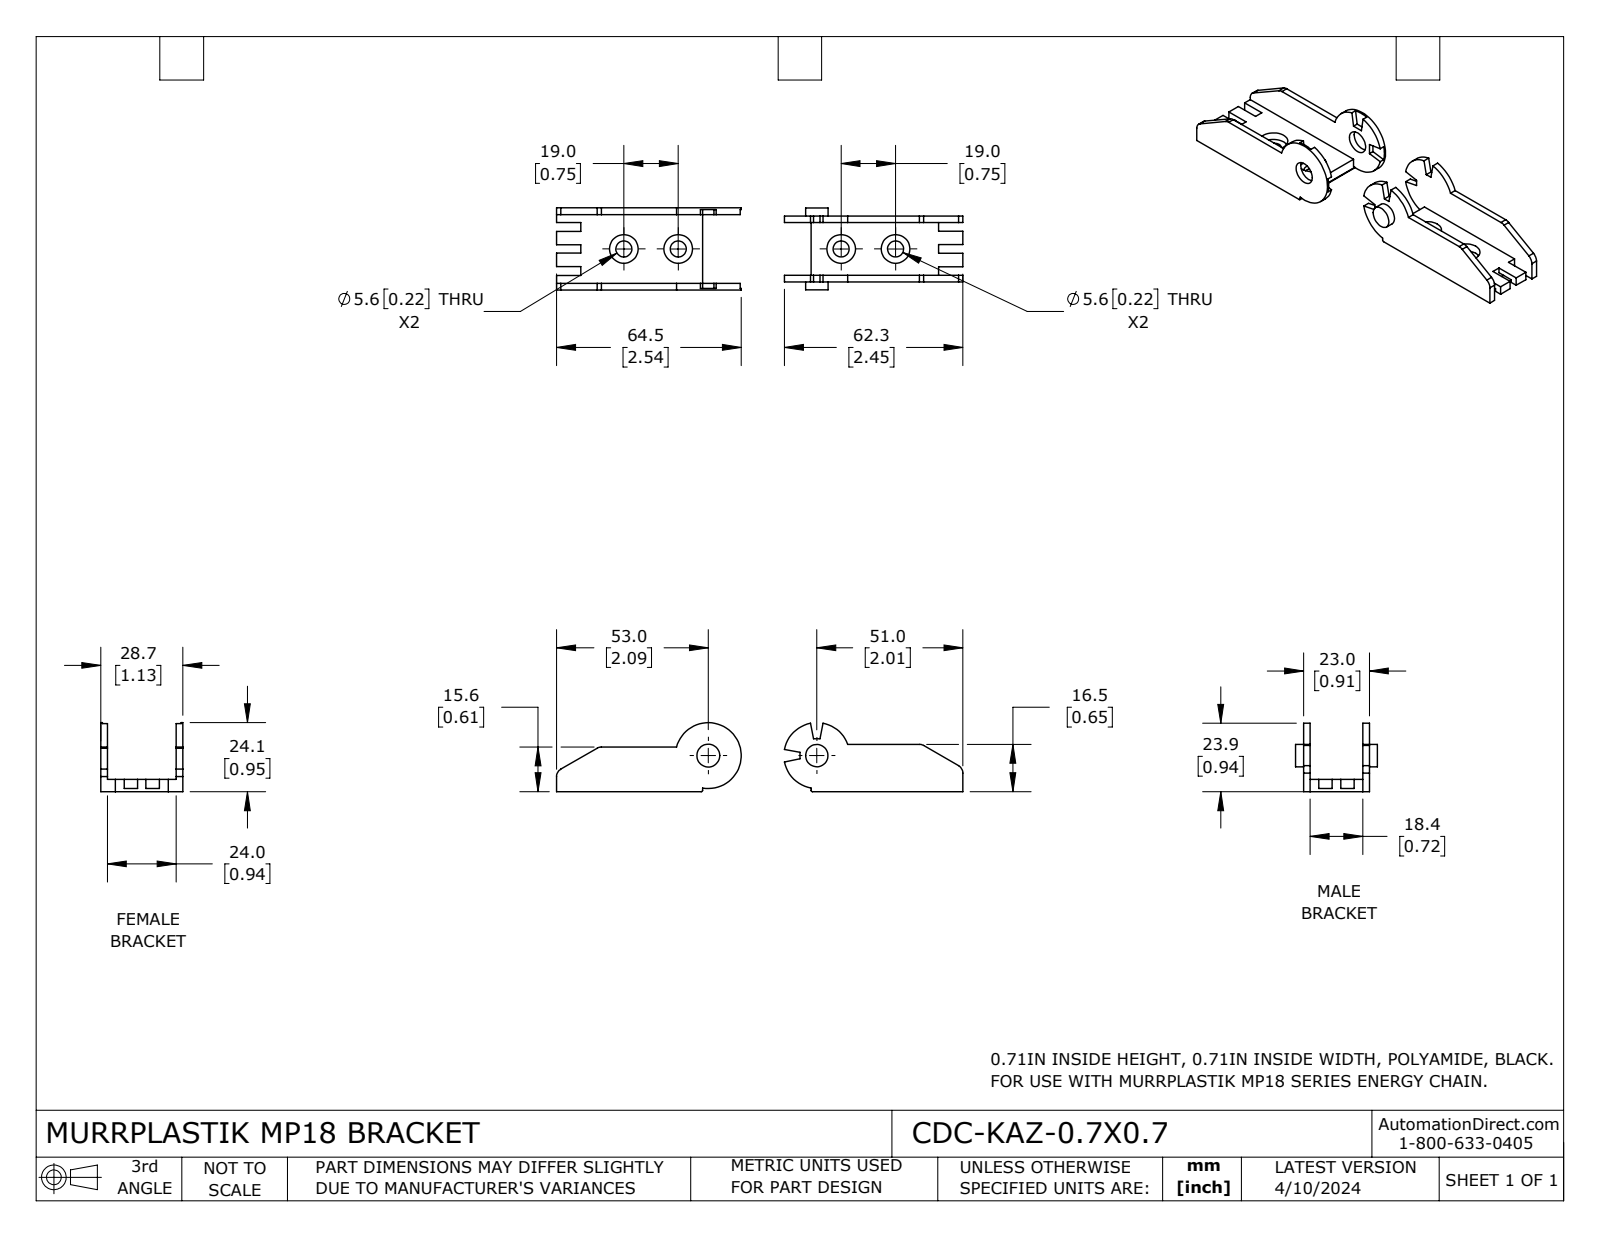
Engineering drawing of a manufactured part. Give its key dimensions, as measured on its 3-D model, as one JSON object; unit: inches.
{"part_name": "CDC-KAZ-0.7X0.7_FEMALE; CDC-KAZ-0.7X0.7_MALE; CDC-KAZ-0.7X0.7", "step_written_by": "SolidWorks 2023 (CONFIG_CONTROL_DESIGN)", "units": "inches", "bodies": {"solids": 2, "faces": 132, "planar": 88, "cylindrical": 44, "other": 0}, "overall_size": [5.587, 1.13, 0.949], "volume_in3": 1.028, "surface_area_in2": 21.72, "round_holes": [[0.22, 4], [0.394, 4], [0.315, 1]], "round_bosses_or_shafts": [[0.307, 1]], "partial_cylinders_radius": [[0.118, 4], [0.02, 2], [0.453, 2]], "face_to_face_distances": [0.112, 1.018, 0.091, 0.169, 0.927, 0.203, 0.815, 0.11, 0.925, 0.093], "hole_center_spacings": [0.748, 2.988, 2.24, 3.736]}
